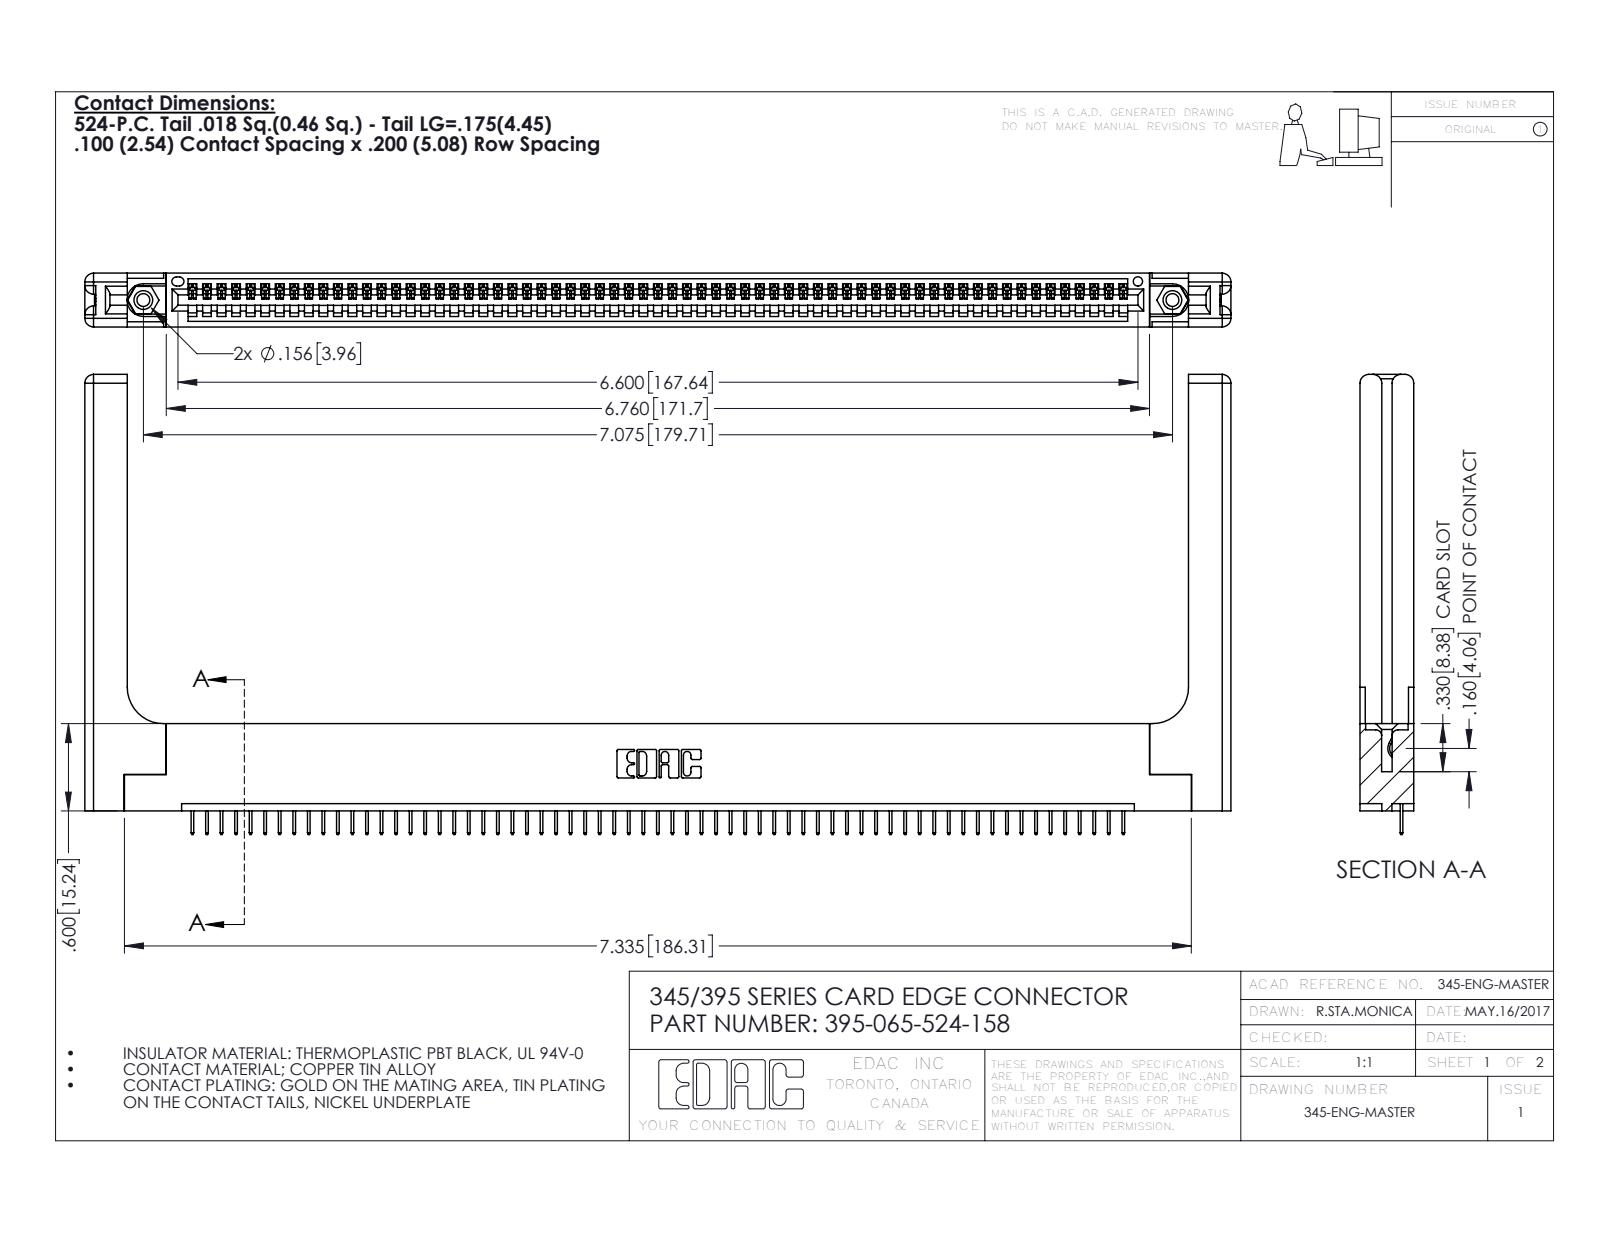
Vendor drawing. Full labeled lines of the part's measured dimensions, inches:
Part name (STEP PRODUCT): 345-250-001_345-250-001-102; 395-065-524-158; 345-220-058_345-220-058; 345 Part_Flush Mounting Lugs - 0.156 Dia-TH (+1 more)
STEP written by: SolidWorks 2016 (CONFIG_CONTROL_DESIGN)
Units: inches
Bodies: 70 solids, 4412 faces (3218 planar, 1134 cylindrical, 60 other)
Overall size (bounding box): 7.879 × 3.162 × 0.37
Volume: 1.675 in³ · Surface area: 46.45 in²
Round holes (diameter × count): ⌀0.089 ×2, ⌀0.125 ×2, ⌀0.156 ×2, ⌀0.064 ×1
Round bosses / shafts (diameter × count): ⌀0.155 ×2
Partial cylindrical surfaces — rounded edges, fillets, slot ends (radius × count): R0.006 ×130, R0.01 ×22, R0.06 ×16, R0.007 ×6, R0.031 ×6, R0.026 ×3, R0.03 ×2, R0.031 ×2
Main face-to-face distances: 0.072, 0.37, 0.298, 0.2, 0.098, 0.272, 0.025, 0.225, 0.148, 0.15
Hole centre spacings: 0.27, 6.839, 7.075
